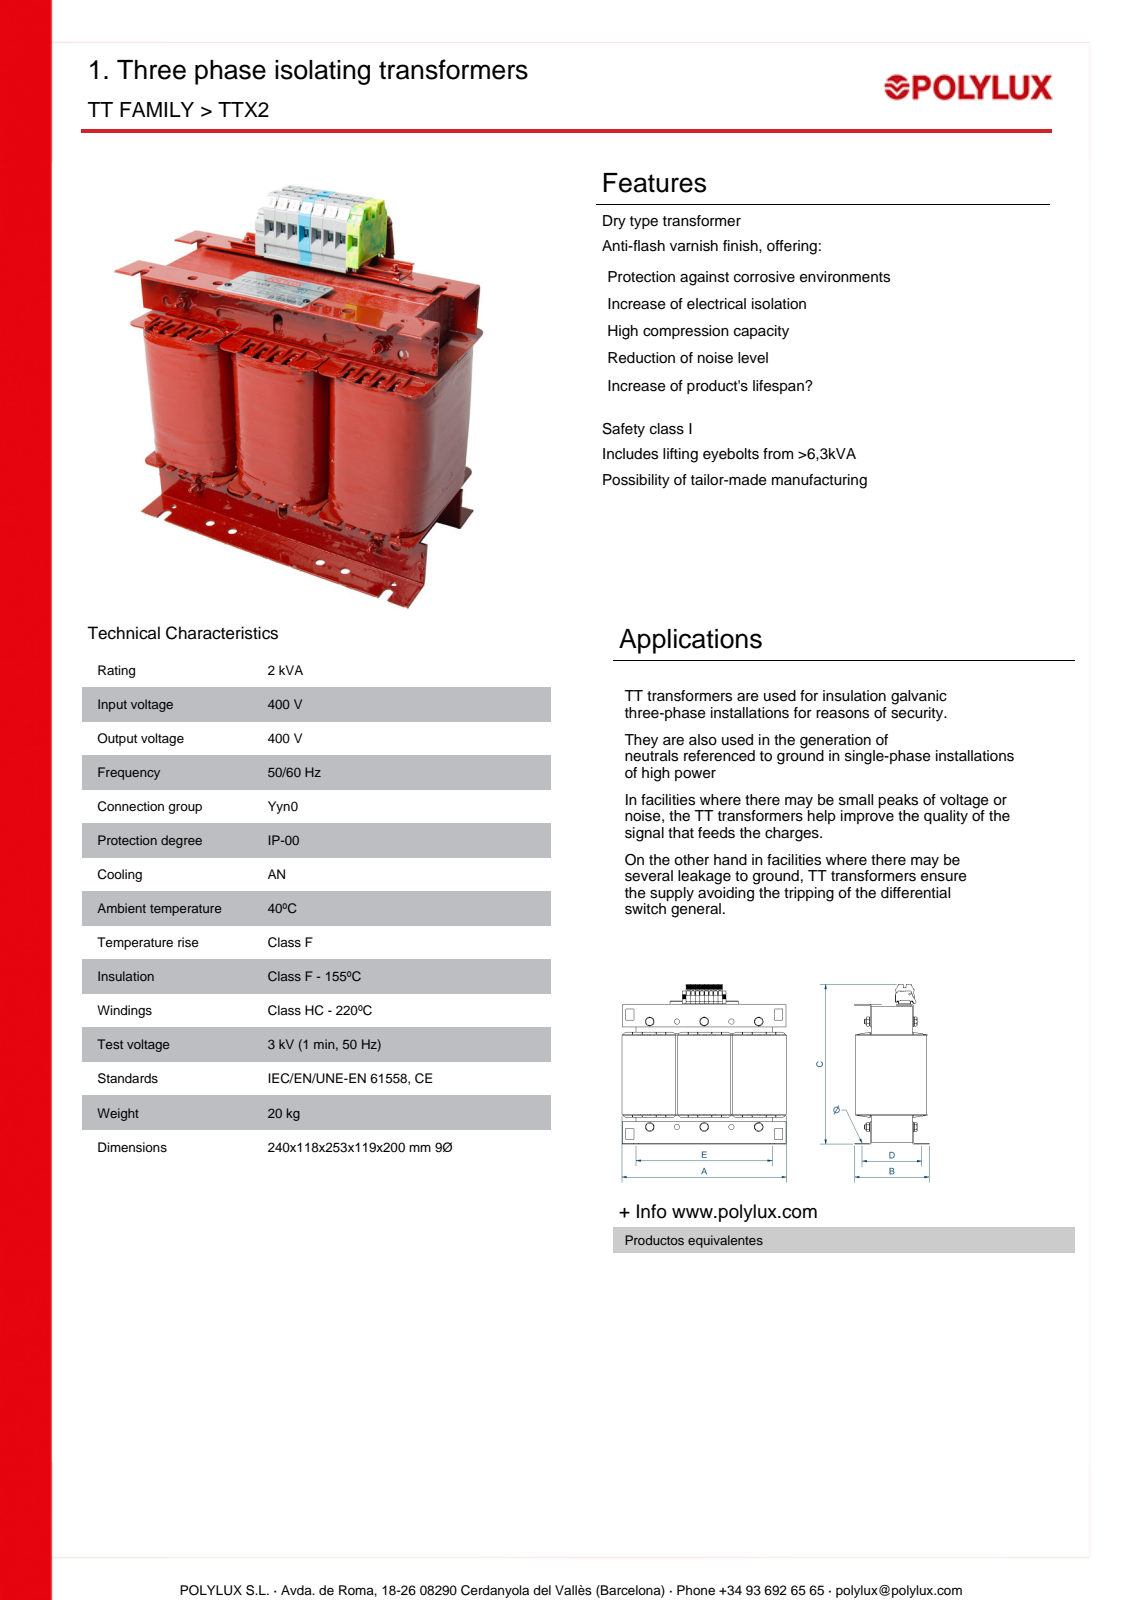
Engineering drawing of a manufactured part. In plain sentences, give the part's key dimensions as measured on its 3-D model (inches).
The part is named "TTX2; Núcleo RC40x75; BRI40-3IP025; BOBINA+CARRETE-RC40X75 (+8 more)". Its 3-D file was written by "Autodesk Inventor 2018 (AUTOMOTIVE_DESIGN)". It is 37 solids with 2524 faces: 1754 planar, 746 cylindrical and 24 other. Overall it measures 10.563 by 9.449 by 5.63 inches. Its volume is 270.7 cubic inches and its surface area 1 338 square inches. Round holes: 18 of diameter 0.276, 16 of diameter 0.169, 6 of diameter 0.138, 6 of diameter 0.194, 6 of diameter 0.354, 4 of diameter 0.163, 4 of diameter 0.209, 1 of diameter 0.118, 1 of diameter 0.228. Round bosses or shafts: 4 of diameter 0.394, 4 of diameter 0.197. Partial cylindrical surfaces (rounded edges, fillets, slot ends): 36 of radius 0.118, 33 of radius 0.02, 24 of radius 0.236, 17 of radius 0.079, 16 of radius 0.157, 16 of radius 0.945, 13 of radius 0.004, 12 of radius 0.012. The main face-to-face distances are 3.15, 0.079, 0.098, 1.673, 6.299, 0.728, 0.65, 2.421, 3.031, 6.201. The hole center spacings are 0.236, 0.658, 0.472, 0.775, 1.577, 6.417, 6.299, 0.435.
